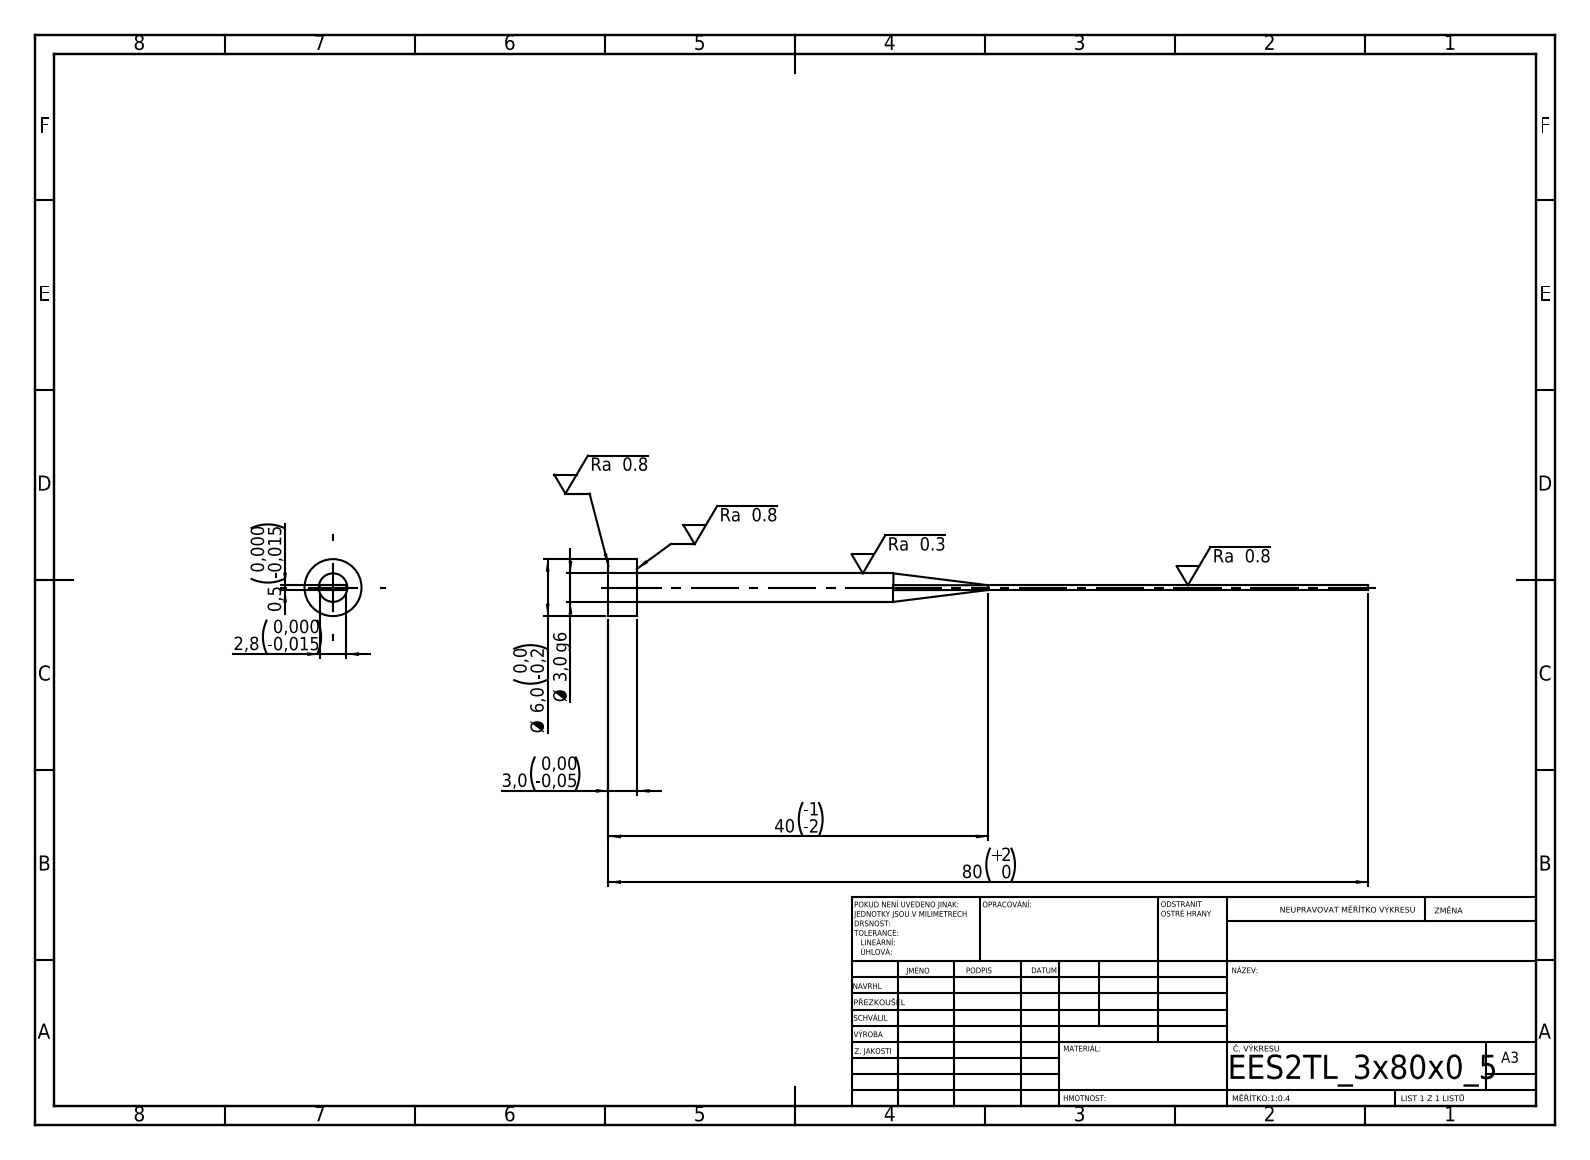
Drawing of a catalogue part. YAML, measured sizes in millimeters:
step_written_by: "SolidWorks 2019 (CONFIG_CONTROL_DESIGN)"
units: millimeters
bodies: {solids: 1, faces: 15, planar: 7, cylindrical: 4, other: 4}
overall_size: [80, 6, 6]
volume: 372
surface_area: 703
round_bosses_or_shafts:
  - {diameter: 6, count: 1}
  - {diameter: 3, count: 1}
face_to_face_distances: [0.5, 3, 2.8, 80, 77]
